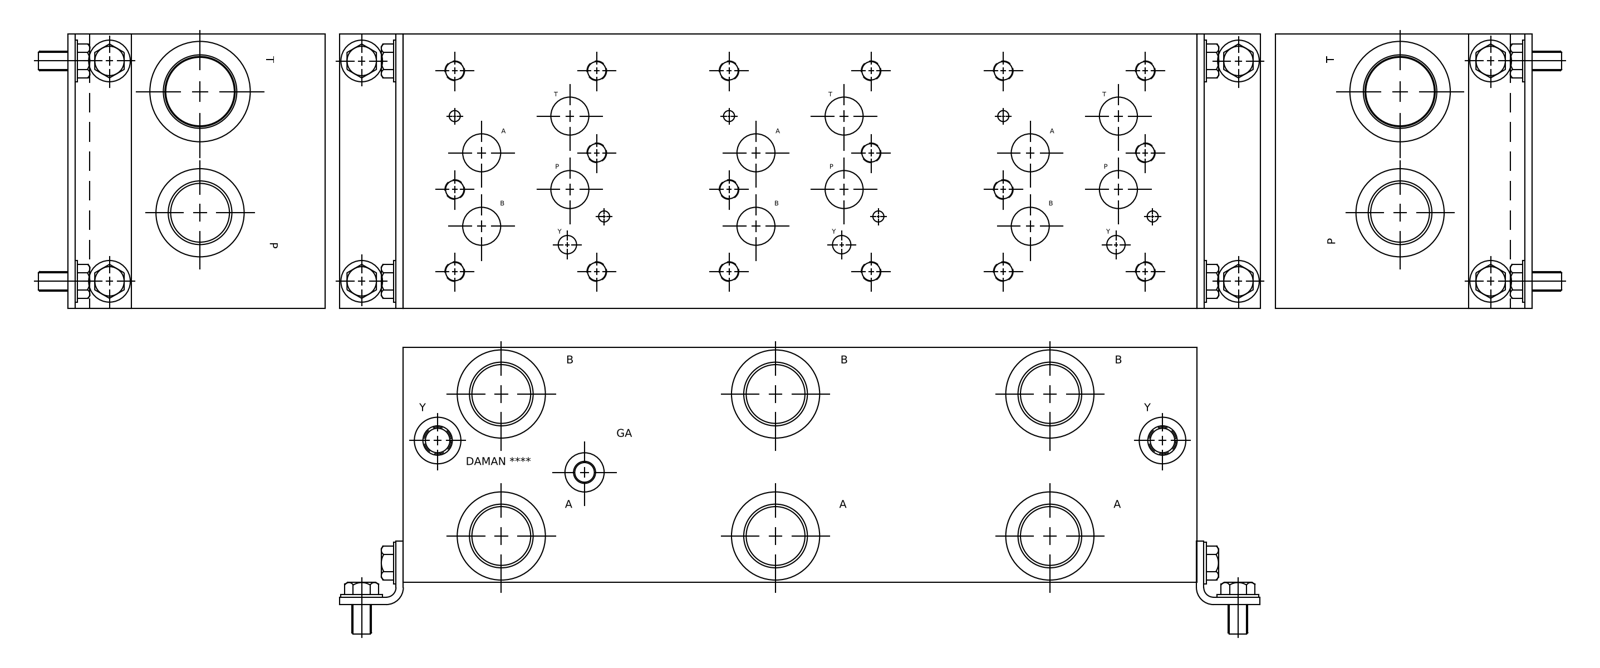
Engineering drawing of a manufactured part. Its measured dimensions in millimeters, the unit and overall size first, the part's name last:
Units: millimetres
Overall size (bounding box): 514.35 × 177.8 × 152.4
Round holes (diameter × count): ⌀10.72 ×21, ⌀12.7 ×20, ⌀24.61 ×12, ⌀39.22 ×7, ⌀58.57 ×7, ⌀7.14 ×6, ⌀36.91 ×6, ⌀41.27 ×6, ⌀43.51 ×6, ⌀11.13 ×3, ⌀14.27 ×3, ⌀17.5 ×2
Main face-to-face distances: 152.4, 177.8, 514.35, 0.79, 177.01, 513.56, 512.77, 19.05, 19.84, 157.96
Hole centre spacings: 177.8, 184.07, 29.53, 47.62, 61.92, 122.98, 355.6, 74.63
Volume: 13 220 000 mm³ · Surface area: 488 719 mm²
Bodies: 1 solid, 826 faces (427 planar, 130 cylindrical, 269 other)
Part name (STEP PRODUCT): Part_AD08HP037S_3D
STEP written by: Autodesk Inventor 2019 (AUTOMOTIVE_DESIGN)
